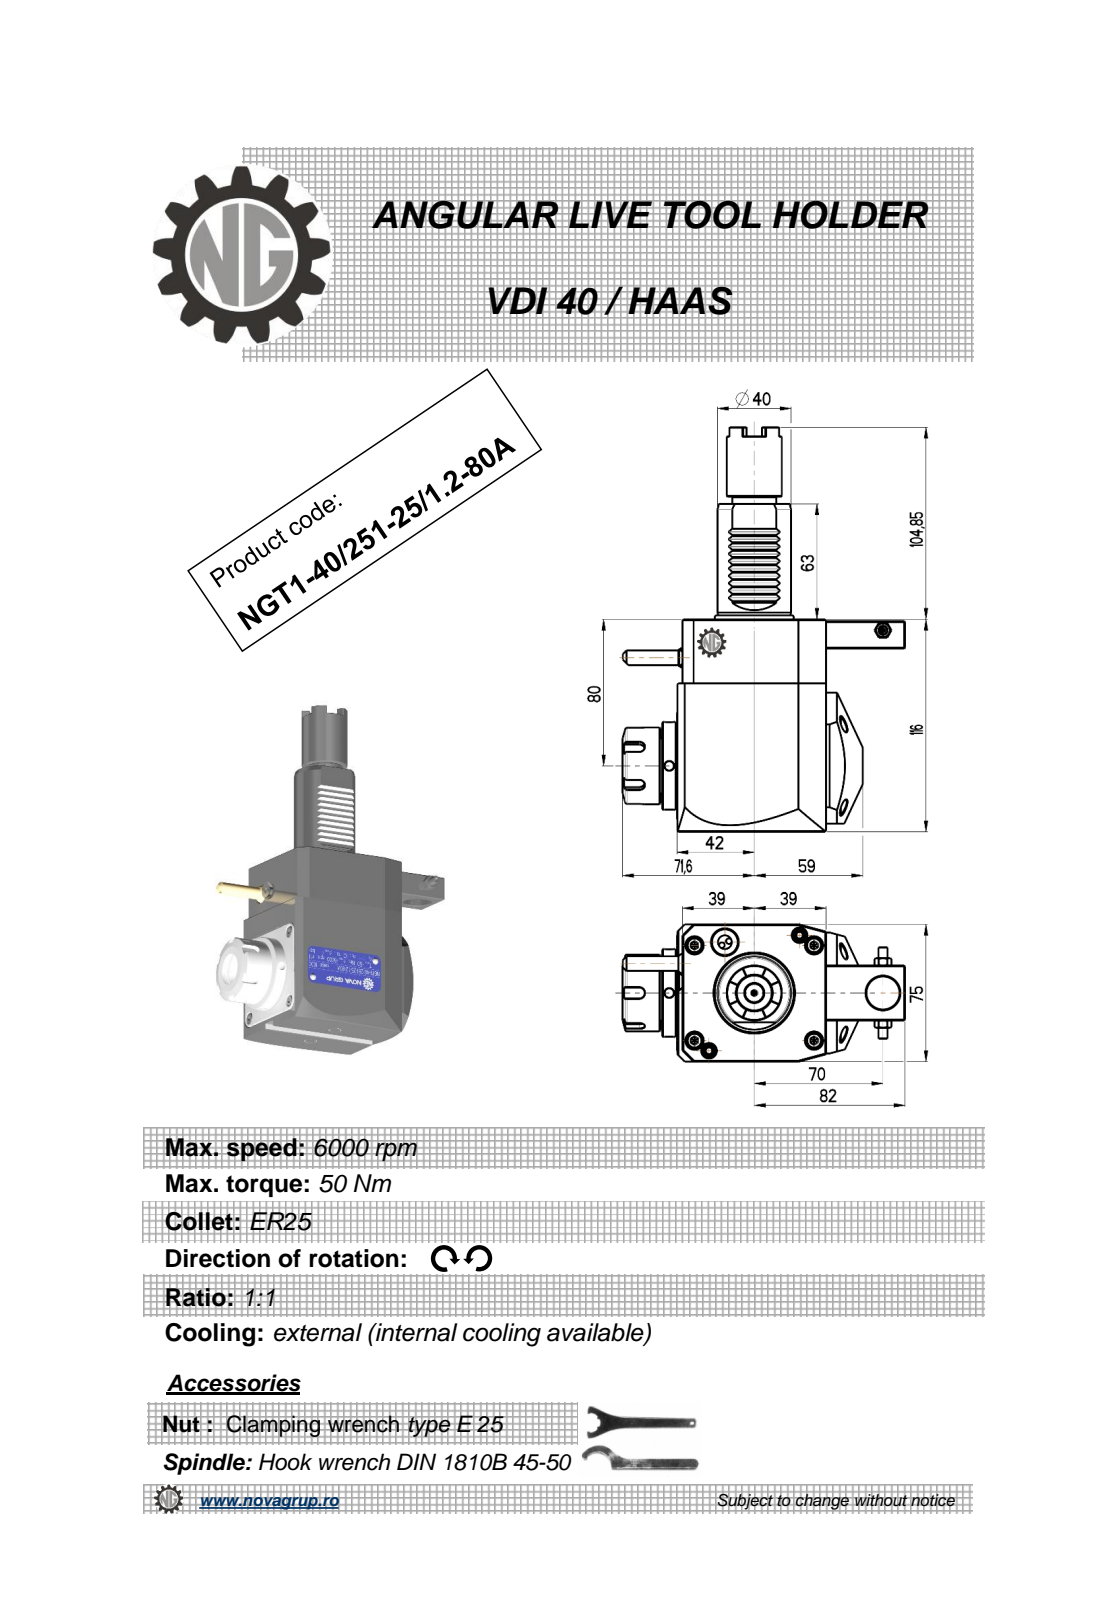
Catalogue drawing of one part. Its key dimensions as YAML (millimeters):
part_name: "NGT1_40_251_25_1_2_80A"
step_written_by: "PRO/ENGINEER BY PARAMETRIC TECHNOLOGY CORPORATION, 2010280 (CONFIG_CONTROL_DESIGN)"
units: millimeters
bodies: {solids: 1, faces: 476, planar: 223, cylindrical: 94, other: 159}
overall_size: [220.85, 153.6, 76.6]
volume: 893707
surface_area: 75282
round_holes:
  - {diameter: 5, count: 3}
  - {diameter: 3, count: 1}
  - {diameter: 4.2, count: 1}
  - {diameter: 9.5, count: 1}
  - {diameter: 18, count: 1}
  - {diameter: 20.3, count: 1}
round_bosses_or_shafts:
  - {diameter: 48, count: 1}
  - {diameter: 42, count: 1}
  - {diameter: 40, count: 1}
  - {diameter: 37.5, count: 1}
  - {diameter: 33, count: 1}
  - {diameter: 30, count: 1}
  - {diameter: 24, count: 1}
  - {diameter: 10, count: 1}
partial_cylinders:
  - {radius: 0.26, count: 12}
  - {radius: 0.3, count: 10}
  - {radius: 0.2, count: 6}
  - {radius: 3, count: 5}
  - {radius: 0.5, count: 1}
  - {radius: 9.75, count: 1}
  - {radius: 40, count: 1}
face_to_face_distances: [75, 116, 81, 3, 78, 2.8, 80.8, 1, 11, 22.5]
hole_center_spacings: [20.93, 61.13, 72.5, 116.25, 137.8]
